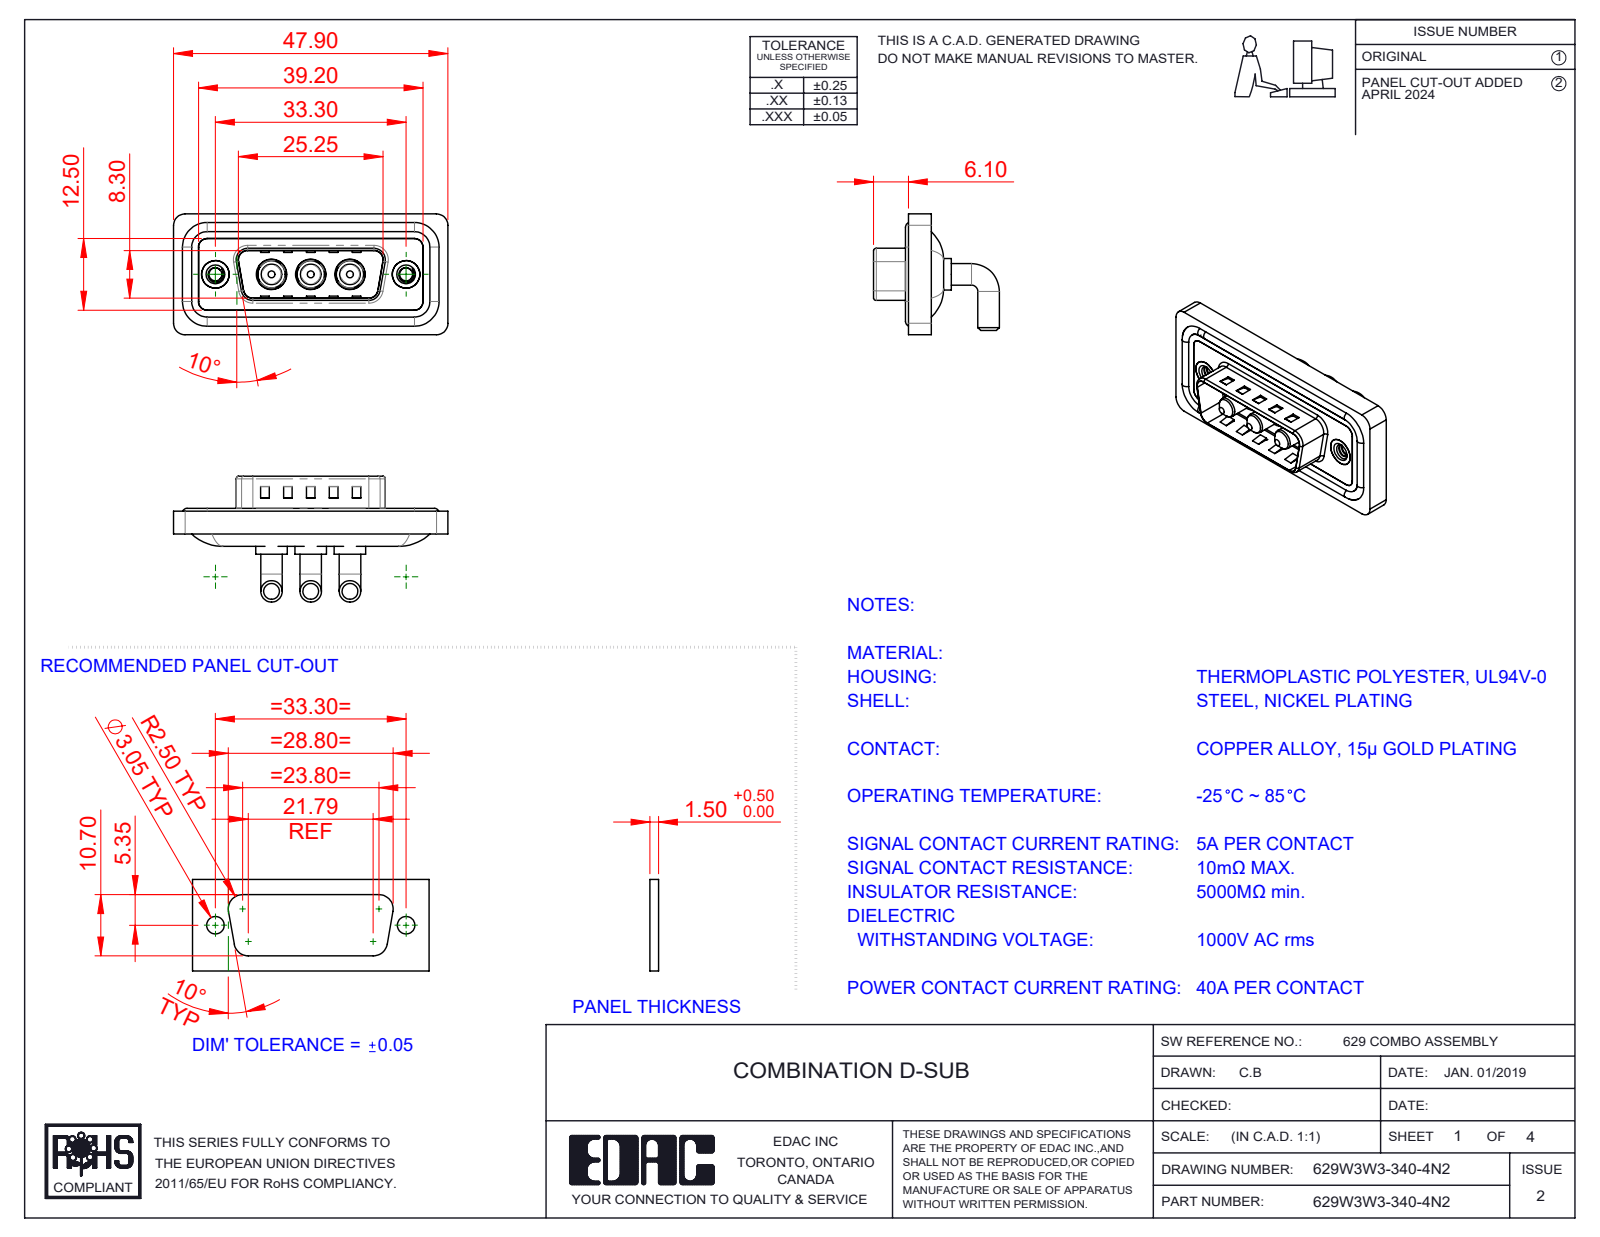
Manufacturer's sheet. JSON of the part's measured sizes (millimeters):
{"part_name": "629Combo Shell Rear_15 Contacts; Power Pin_40A RA; 629Combo Shell Front_15 Contacts; 629Combo Threaded Rivet_2 (+3 more)", "step_written_by": "SolidWorks 2023 (CONFIG_CONTROL_DESIGN)", "units": "millimeters", "bodies": {"solids": 13, "faces": 576, "planar": 207, "cylindrical": 247, "other": 122}, "overall_size": [47.9, 21.98, 21.1], "volume_mm3": 6008, "surface_area_mm2": 9168, "round_holes": [[4.85, 3], [5.3, 3], [2.26, 2], [4, 2], [4.8, 2], [5, 2]], "round_bosses_or_shafts": [[3.75, 6], [1.6, 4], [5.5, 3], [5.2, 3], [4.75, 3], [3.6, 3], [4.9, 2]], "partial_cylinders_radius": [[2, 20], [1.5, 18], [0.5, 8], [1.6, 8], [0.25, 4], [0.6, 4], [0.65, 4], [0.9, 4]], "face_to_face_distances": [0.4, 2.9, 0.8, 1.1, 2.1, 1.6, 3.1, 2.5, 4.5, 3.7], "hole_center_spacings": [6.85, 9.8, 16.65, 23.5, 13.7, 33.3]}
